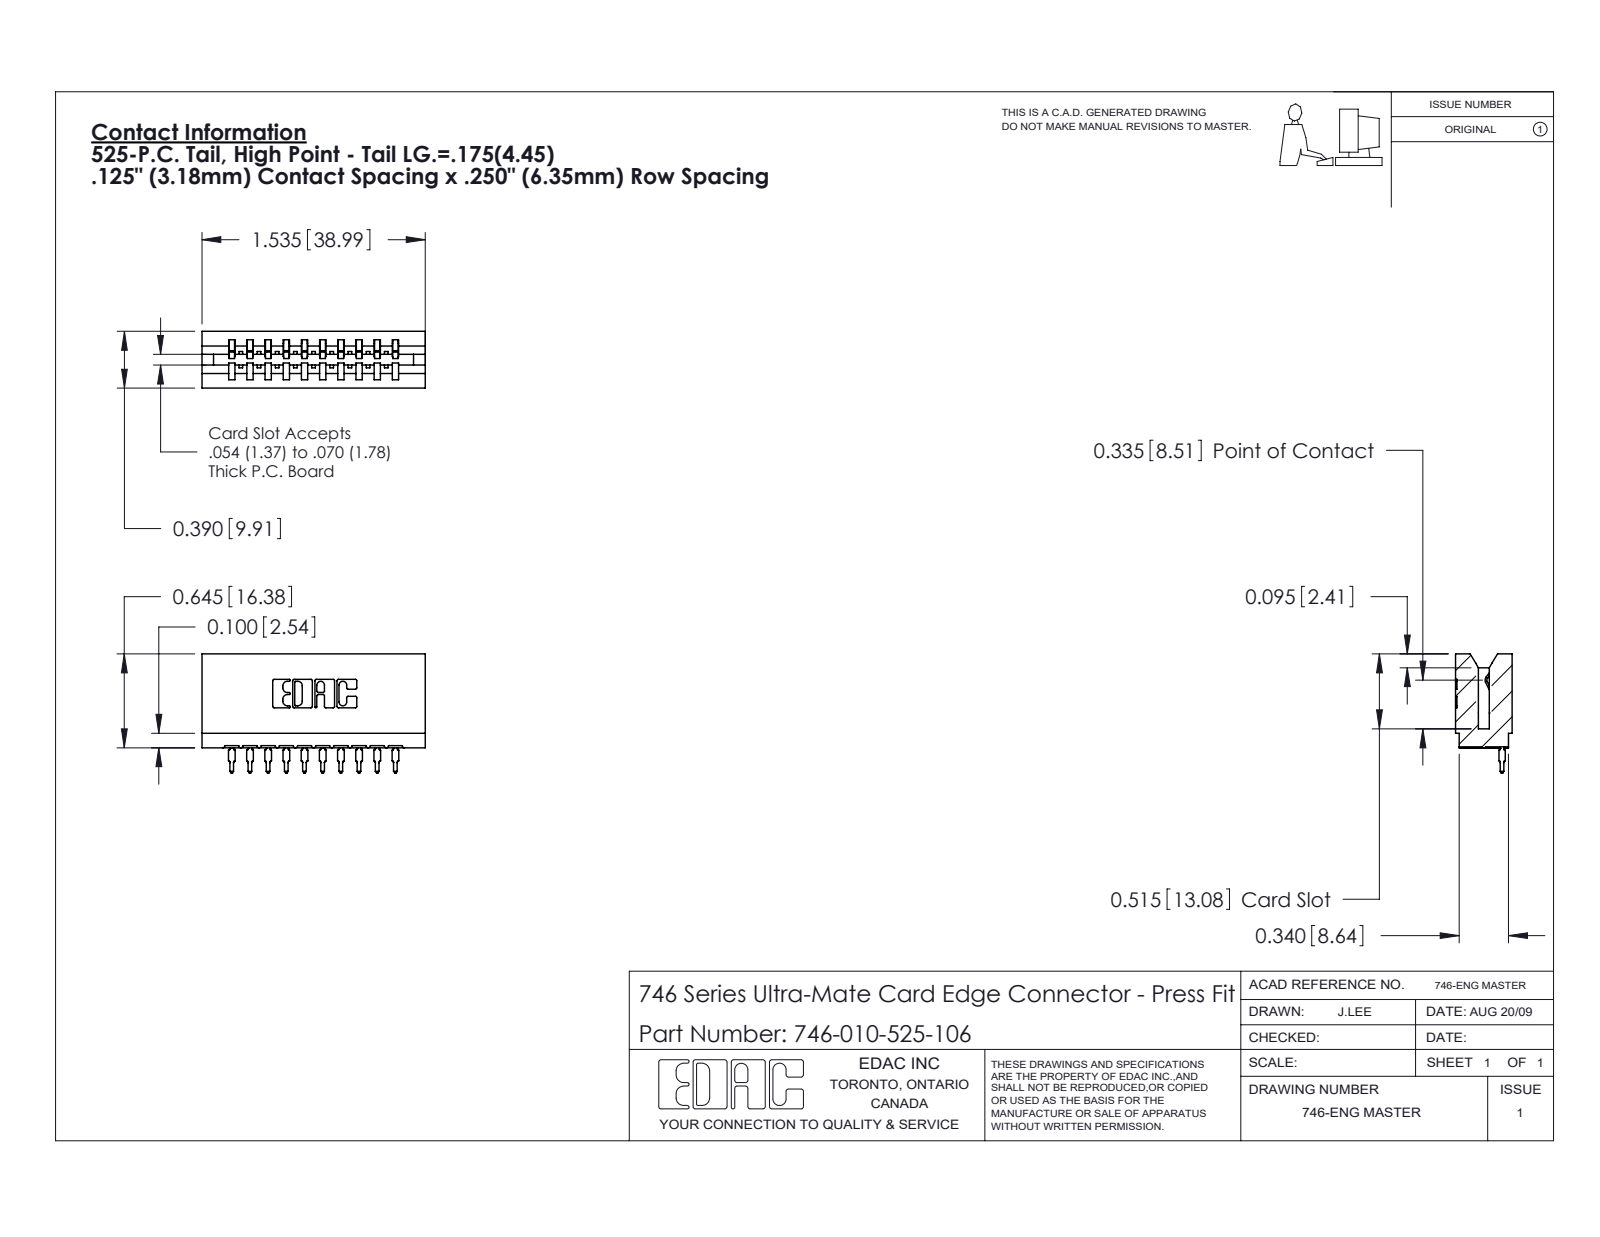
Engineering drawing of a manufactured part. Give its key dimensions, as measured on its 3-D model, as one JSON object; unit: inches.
{"part_name": "746-292-001_525; 746 Part_.515 Slot Depth - 06; 746-010-525-106", "step_written_by": "SolidWorks 2020 (CONFIG_CONTROL_DESIGN)", "units": "inches", "bodies": {"solids": 11, "faces": 1178, "planar": 686, "cylindrical": 232, "other": 260}, "overall_size": [1.535, 0.819, 0.39], "volume_in3": 0.26, "surface_area_in2": 8.895, "partial_cylinders_radius": [[0.01, 22], [0.021, 20], [0.015, 11], [0.007, 6], [0.031, 6], [0.005, 4], [0.011, 4], [0.026, 3]], "face_to_face_distances": [0.25, 0.5, 0.333, 0.042, 0.125, 0.057, 0.292, 0.75, 0.39, 0.375]}
